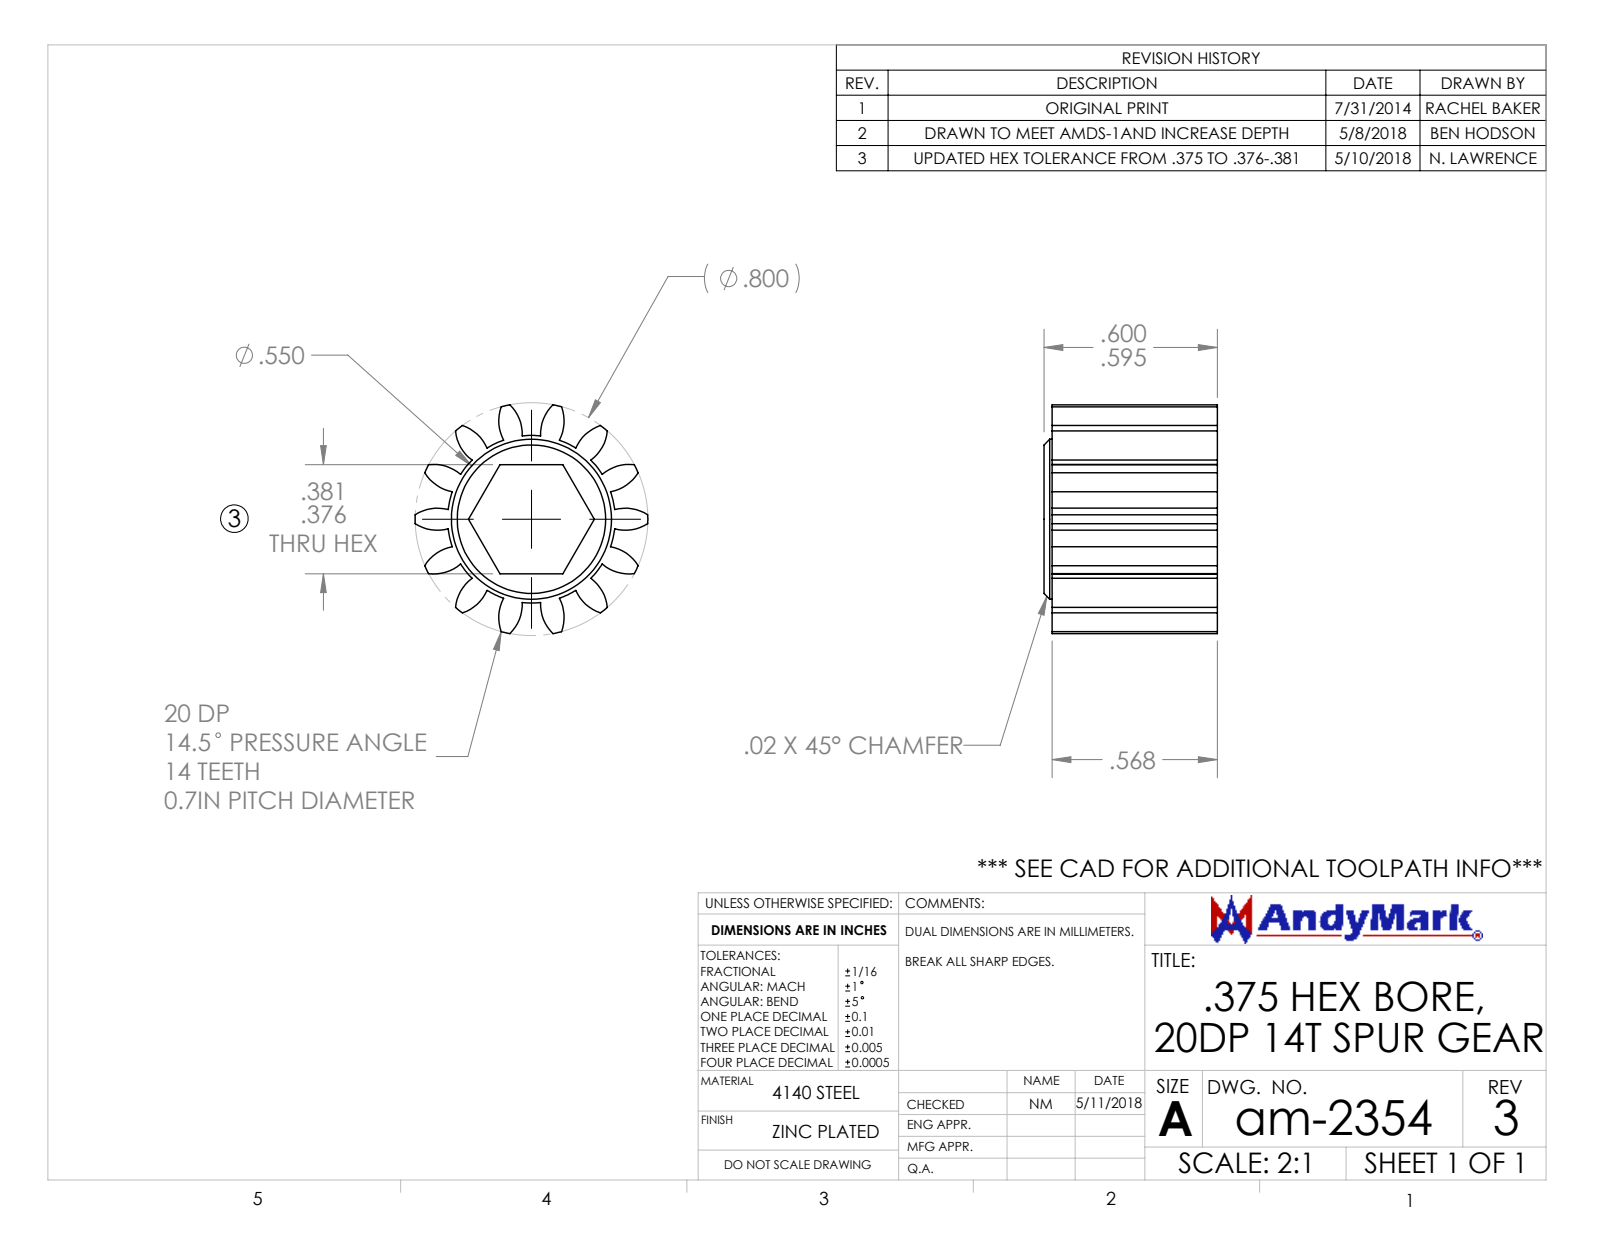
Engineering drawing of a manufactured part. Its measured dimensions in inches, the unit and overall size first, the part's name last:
Units: inches
Overall size (bounding box): 0.8 × 0.786 × 0.596
Round bosses / shafts (diameter × count): ⌀0.55 ×1
Partial cylindrical surfaces — rounded edges, fillets, slot ends (radius × count): R0.14 ×28, R0.288 ×1, R0.4 ×1
Main face-to-face distances: 0.375, 0.568, 0.596, 0.028
Volume: 0.14 in³ · Surface area: 3.912 in²
Bodies: 1 solid, 74 faces (9 planar, 63 cylindrical, 2 other)
Part name (STEP PRODUCT): am-2354 14T 20dp 375hex REV3
STEP written by: SolidWorks 2017 (AUTOMOTIVE_DESIGN)
